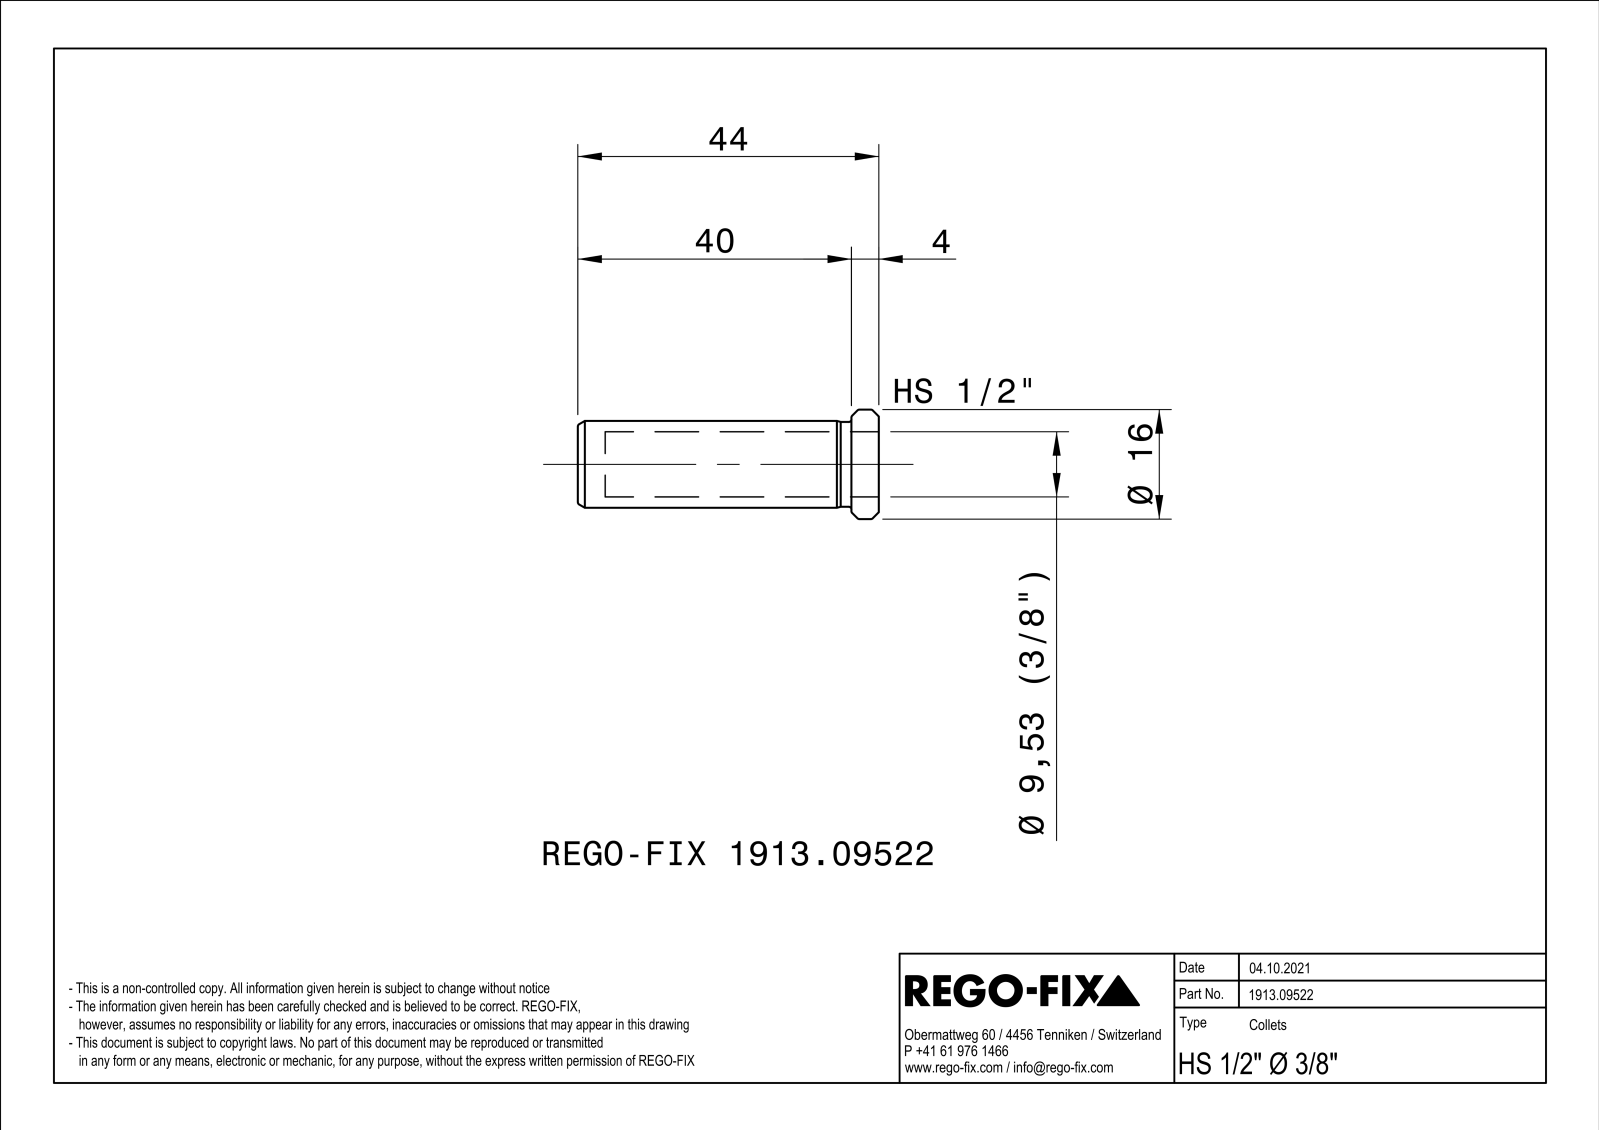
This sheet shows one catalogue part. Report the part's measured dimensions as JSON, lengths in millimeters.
{"part_name": "NOCUT", "step_written_by": "SIEMENS PLM Software Solid Edge ST10 (AUTOMOTIVE_DESIGN)", "units": "millimeters", "bodies": {"solids": 1, "faces": 70, "planar": 22, "cylindrical": 11, "other": 37}, "overall_size": [44, 15.98, 15.98], "volume_mm3": 2442, "surface_area_mm2": 3531, "round_holes": [[9.53, 1], [10.2, 1]], "round_bosses_or_shafts": [[16, 1], [12.7, 1], [12.4, 1]], "face_to_face_distances": [0.8, 4, 44, 40]}
